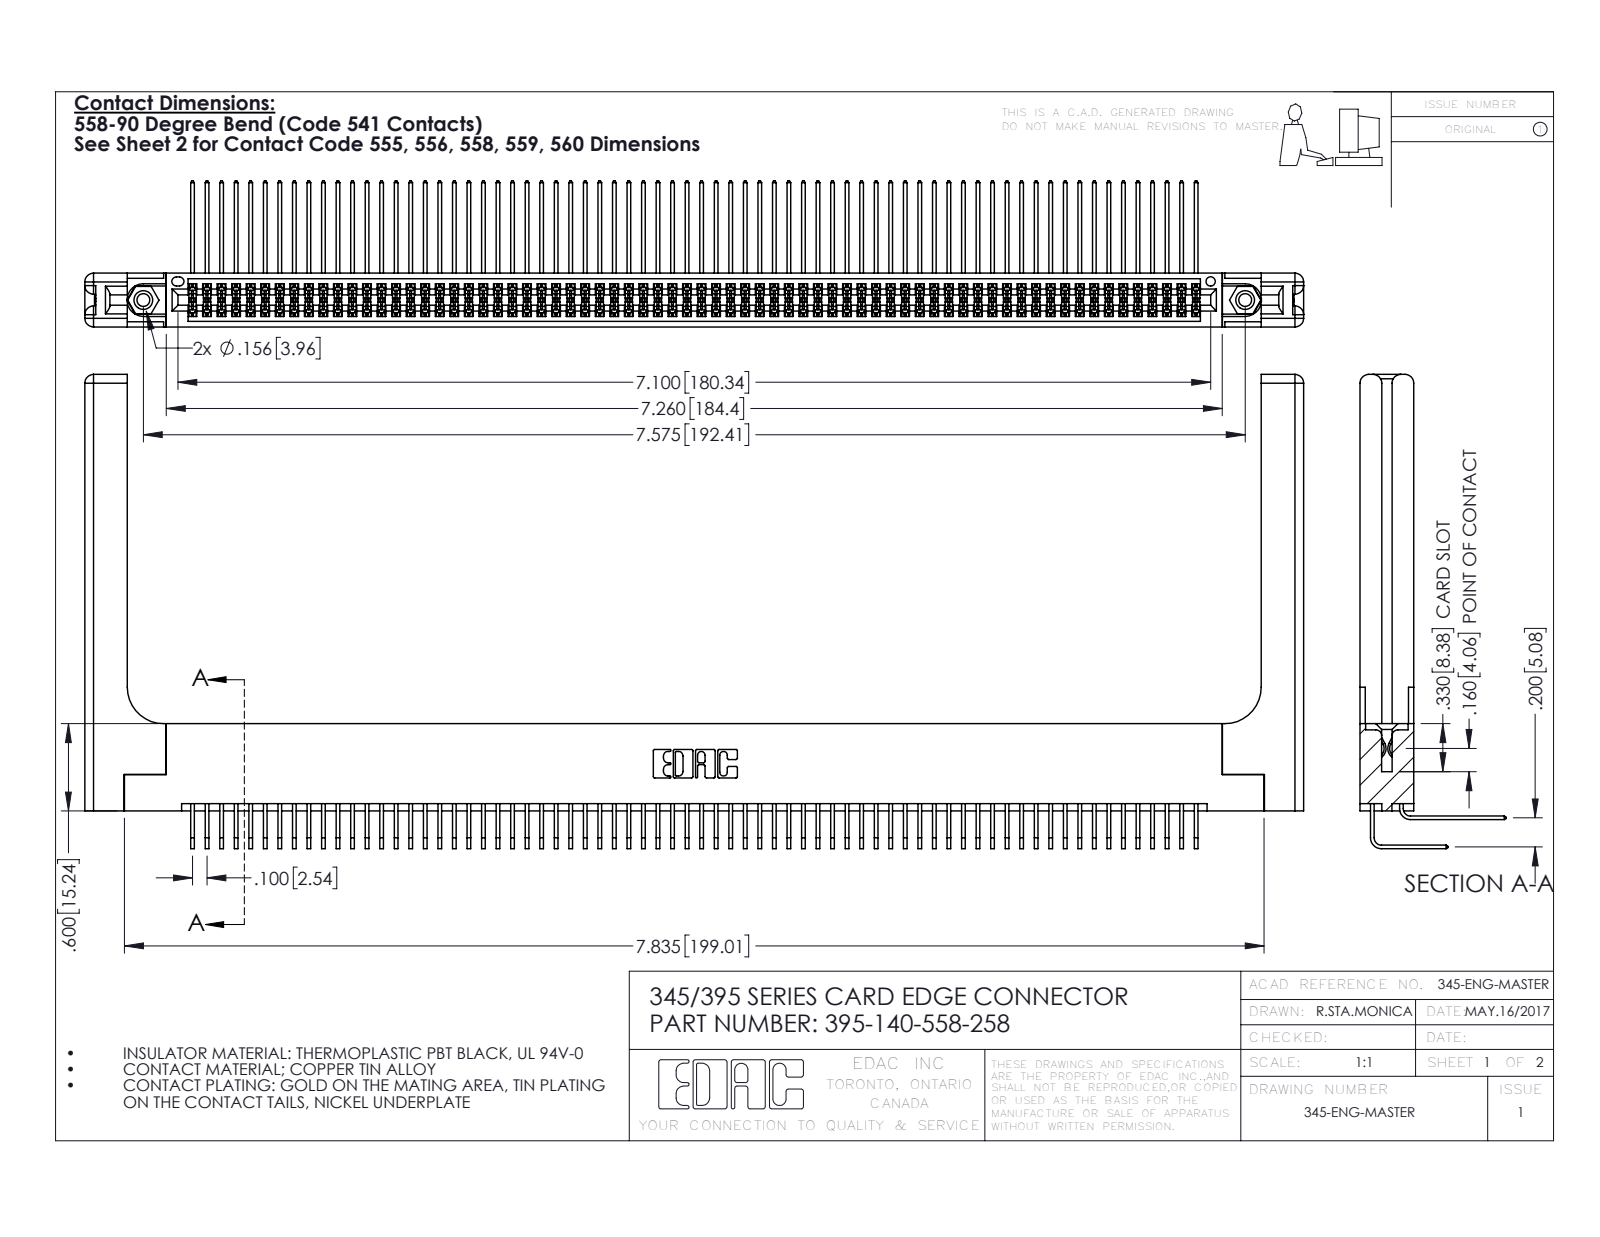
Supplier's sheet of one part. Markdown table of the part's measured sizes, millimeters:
| quantity | value |
| --- | --- |
| part name | 395-140-558-258; 345-292-001_558 Tail - 2; 345-220-058_345-220-058; 345 Part_Flush Mounting Lugs - 0.156 Dia-TH (+2 more) |
| STEP written by | SolidWorks 2016 (CONFIG_CONTROL_DESIGN) |
| units | millimeters |
| bodies | 145 solids, 7662 faces (5128 planar, 2474 cylindrical, 60 other) |
| overall size | 212.8 × 82.8 × 25.5 |
| volume | 30 220 mm³ |
| surface area | 41 540 mm² |
| round holes (diameter × count) | 2.3 × 2, 3.2 × 2, 4 × 2, 1.6 × 1 |
| round bosses / shafts (diameter × count) | 3.9 × 2 |
| partial cylindrical surfaces (radius × count) | 0.2 × 279, 0.3 × 22, 1.5 × 16, 0.2 × 6, 0.8 × 6, 0.7 × 3, 0.4 × 2, 0.5 × 2 |
| main face-to-face distances | 1.8, 7.6, 5.1, 9.4, 2.5, 6.9, 0.6, 5.7, 0.6, 4.4 |
| hole center spacings | 6.9, 186.4, 192.4 |
